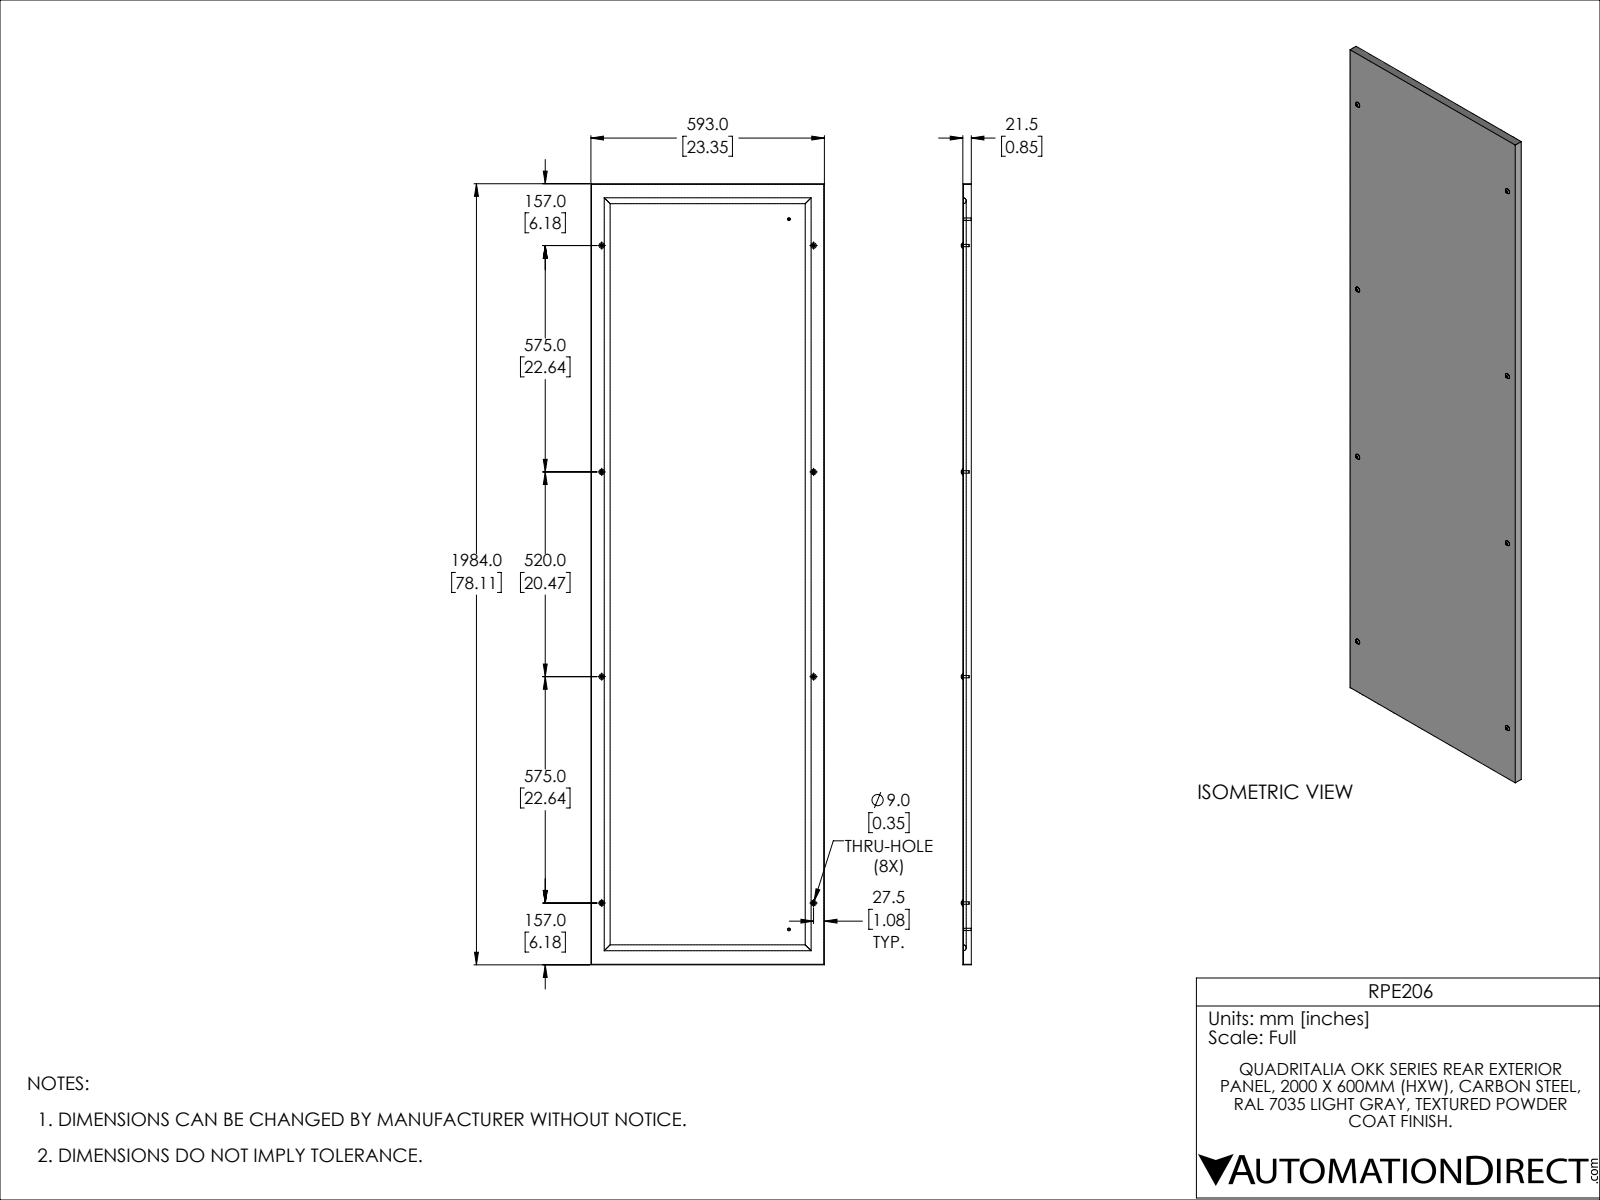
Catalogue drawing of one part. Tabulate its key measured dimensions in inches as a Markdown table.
| quantity | value |
| --- | --- |
| part name | RPE206 |
| STEP written by | SolidWorks 2021 (CONFIG_CONTROL_DESIGN) |
| units | inches |
| bodies | 15 solids, 311 faces (157 planar, 128 cylindrical, 26 other) |
| overall size | 78.11 × 23.346 × 0.992 |
| volume | 141.3 in³ |
| surface area | 4 269 in² |
| round holes (diameter × count) | 0.354 × 8 |
| round bosses / shafts (diameter × count) | 0.236 × 10, 0.551 × 8, 0.276 × 2 |
| partial cylindrical surfaces (radius × count) | 0.02 × 96, 0.296 × 4 |
| main face-to-face distances | 0.059, 23.287, 23.346, 23.228, 78.051, 78.11, 77.992, 0.846, 0.787, 38.606 |
| hole center spacings | 21.181, 22.638, 31.002, 43.11, 48.033, 20.472, 29.458, 65.748 |
